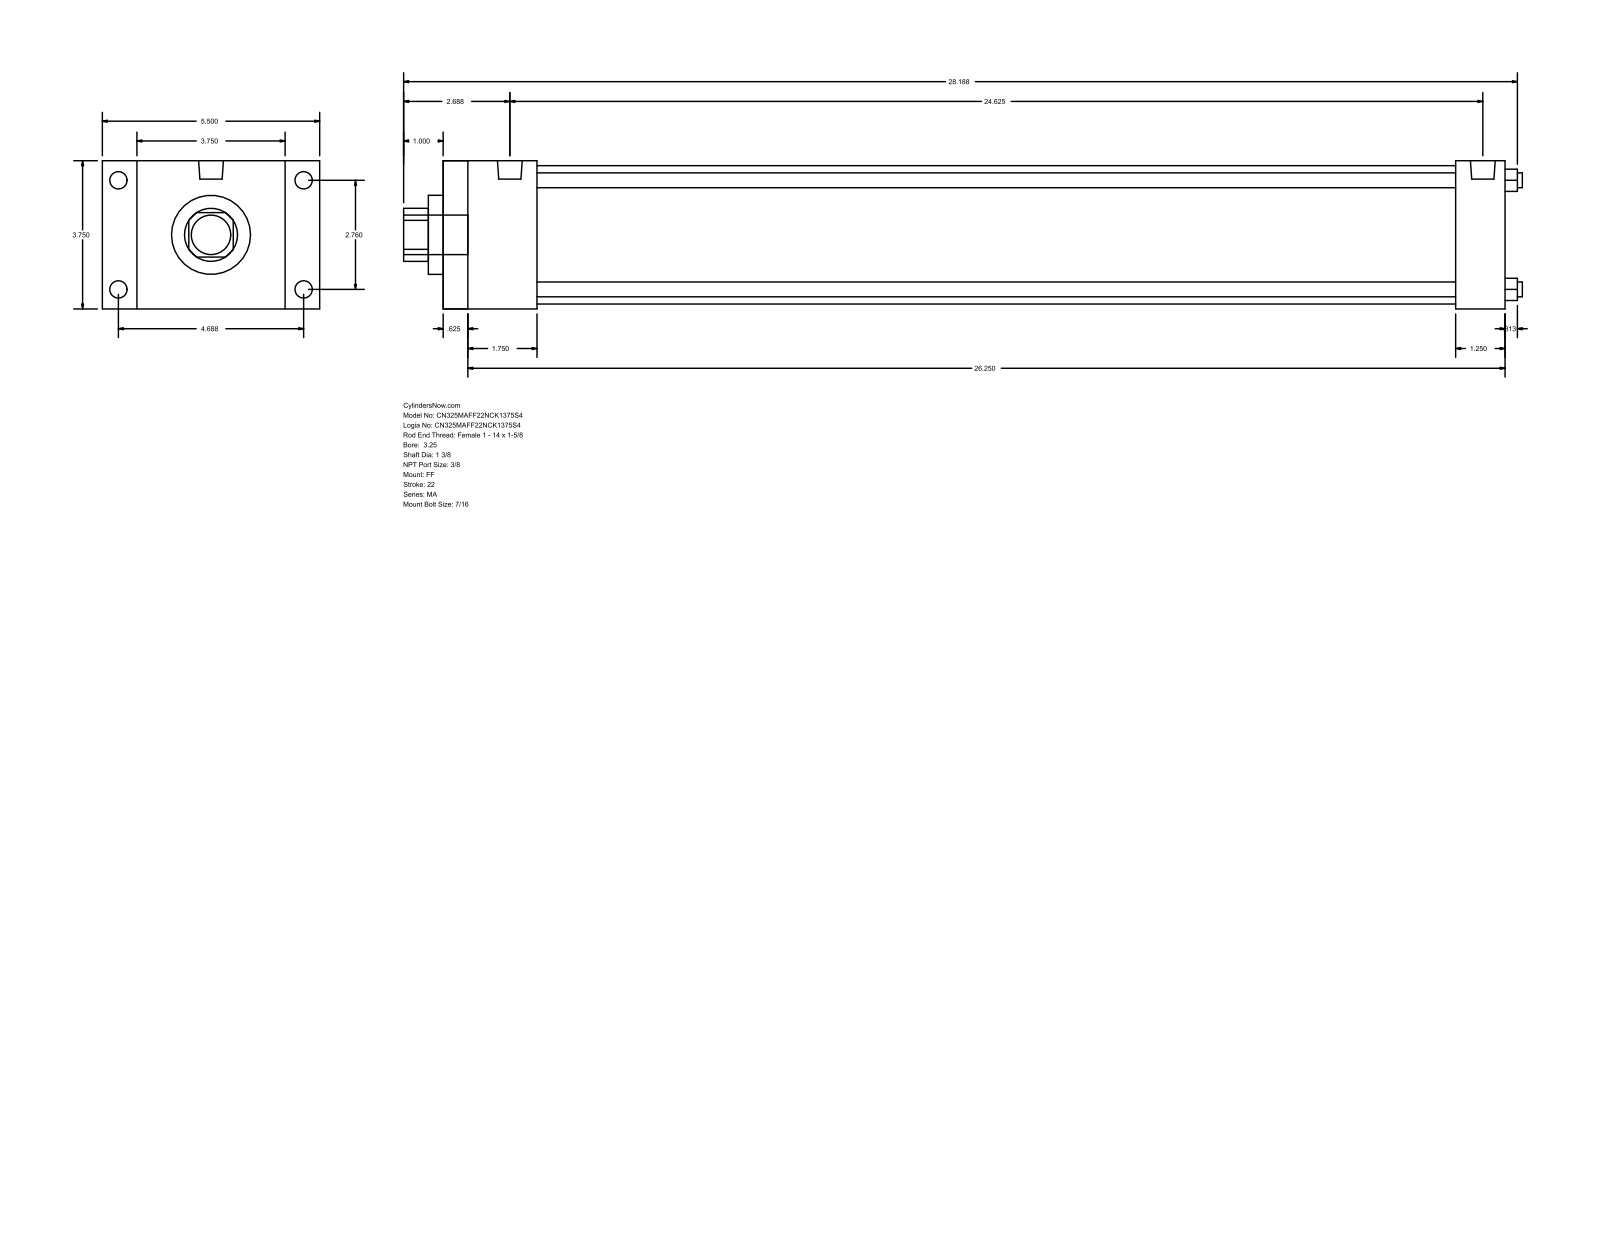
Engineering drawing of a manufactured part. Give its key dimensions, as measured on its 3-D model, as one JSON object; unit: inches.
{"part_name": "MA_FF__0325_1.375", "step_written_by": "GSSL Pune (CONFIG_CONTROL_DESIGN)", "units": "inches", "bodies": {"solids": 0, "faces": 92, "planar": 64, "cylindrical": 28, "other": 0}, "overall_size": [28.313, 5.5, 3.75], "round_holes": [[0.375, 4], [1.375, 1], [2, 1], [3.5, 1]], "round_bosses_or_shafts": [[0.437, 8], [0.627, 2], [1, 1]], "partial_cylinders_radius": [[0.672, 1]], "face_to_face_distances": [3.75, 26.875, 0.625, 26.25, 0.875, 4.625, 2.375, 25.625, 1.75, 25], "hole_center_spacings": [1.952, 2.76, 3.903]}
